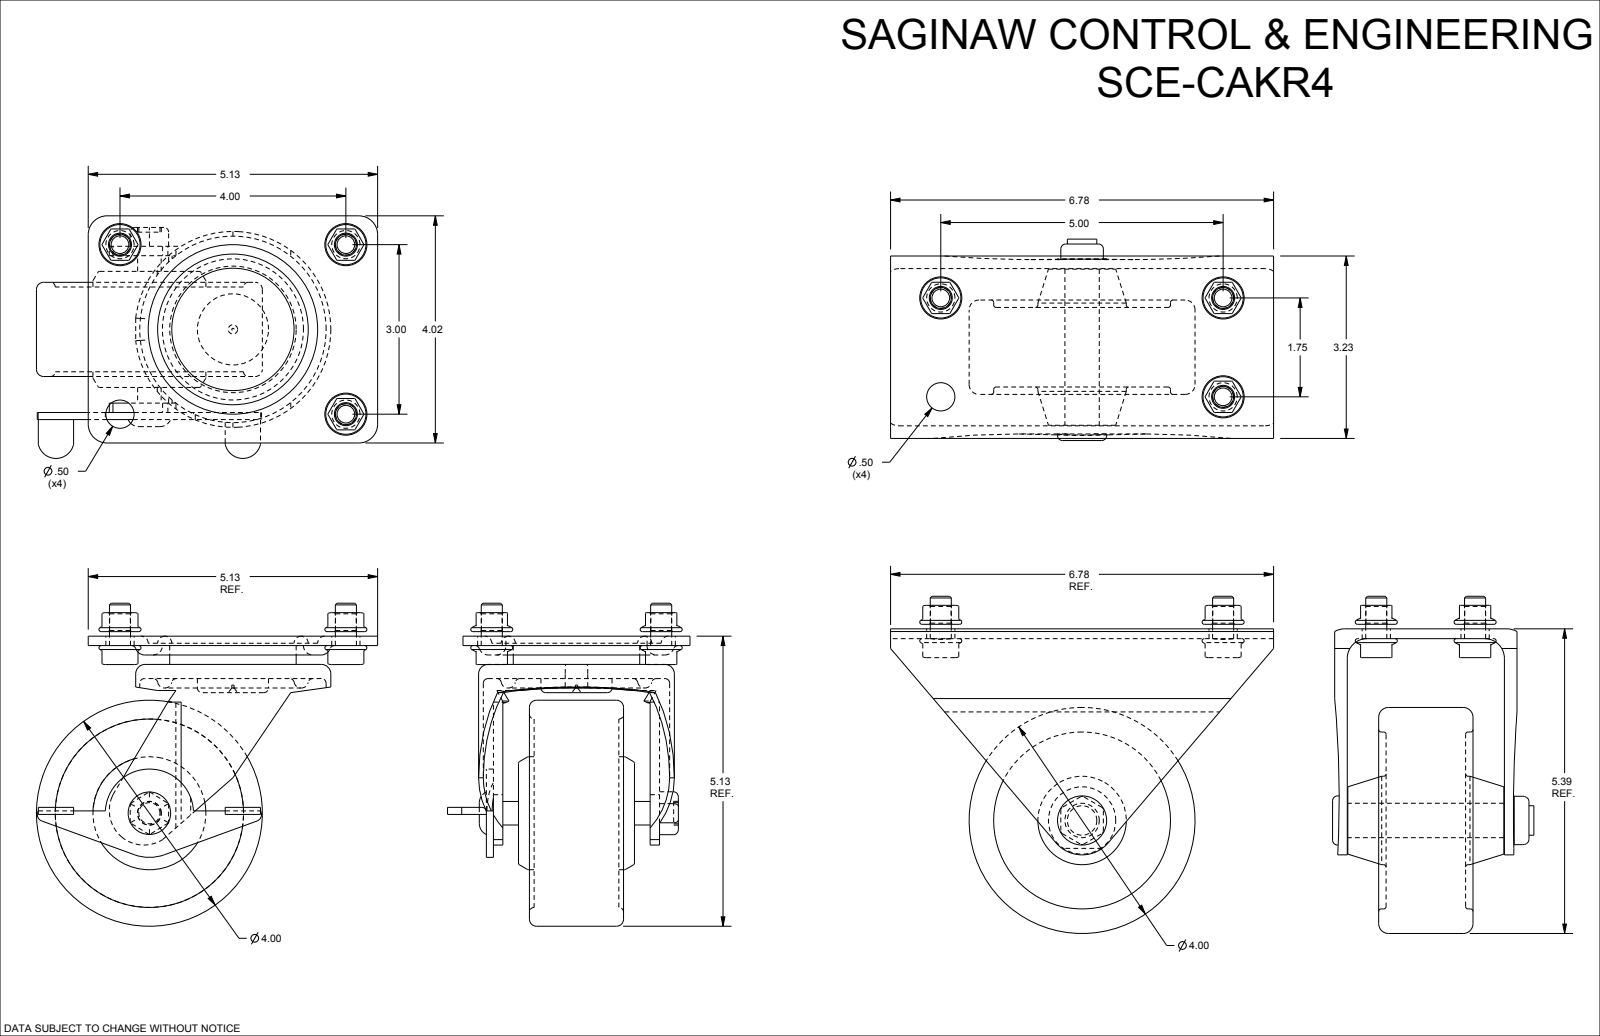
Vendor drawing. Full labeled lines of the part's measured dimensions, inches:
Part name (STEP PRODUCT): SCE-CAKR4
STEP written by: SolidWorks 2019 (CONFIG_CONTROL_DESIGN)
Units: inches
Bodies: 38 solids, 1852 faces (476 planar, 370 cylindrical, 1006 other)
Overall size (bounding box): 26.87 × 24.293 × 5.975
Volume: 125.1 in³ · Surface area: 669.6 in²
Round holes (diameter × count): ⌀0.367 ×16, ⌀0.5 ×16, ⌀0.04 ×2, ⌀3.3 ×2, ⌀0.421 ×1, ⌀0.609 ×1, ⌀3.13 ×1, ⌀4 ×1
Round bosses / shafts (diameter × count): ⌀0.373 ×16, ⌀3.467 ×2, ⌀2.239 ×2, ⌀1.259 ×2, ⌀4 ×1, ⌀2 ×1, ⌀1.565 ×1, ⌀0.87 ×1
Partial cylindrical surfaces — rounded edges, fillets, slot ends (radius × count): R0.01 ×96, R0.083 ×12, R0.087 ×12, R0.333 ×8, R0.348 ×8, R0.043 ×6, R0.32 ×4, R0.08 ×2
Main face-to-face distances: 20, 0.223, 3.006, 0.174, 0.167, 2.783, 0.049, 20.223, 23.006, 19.777
Hole centre spacings: 20, 2.5, 5, 1.75, 3, 4, 5.297, 18.608
